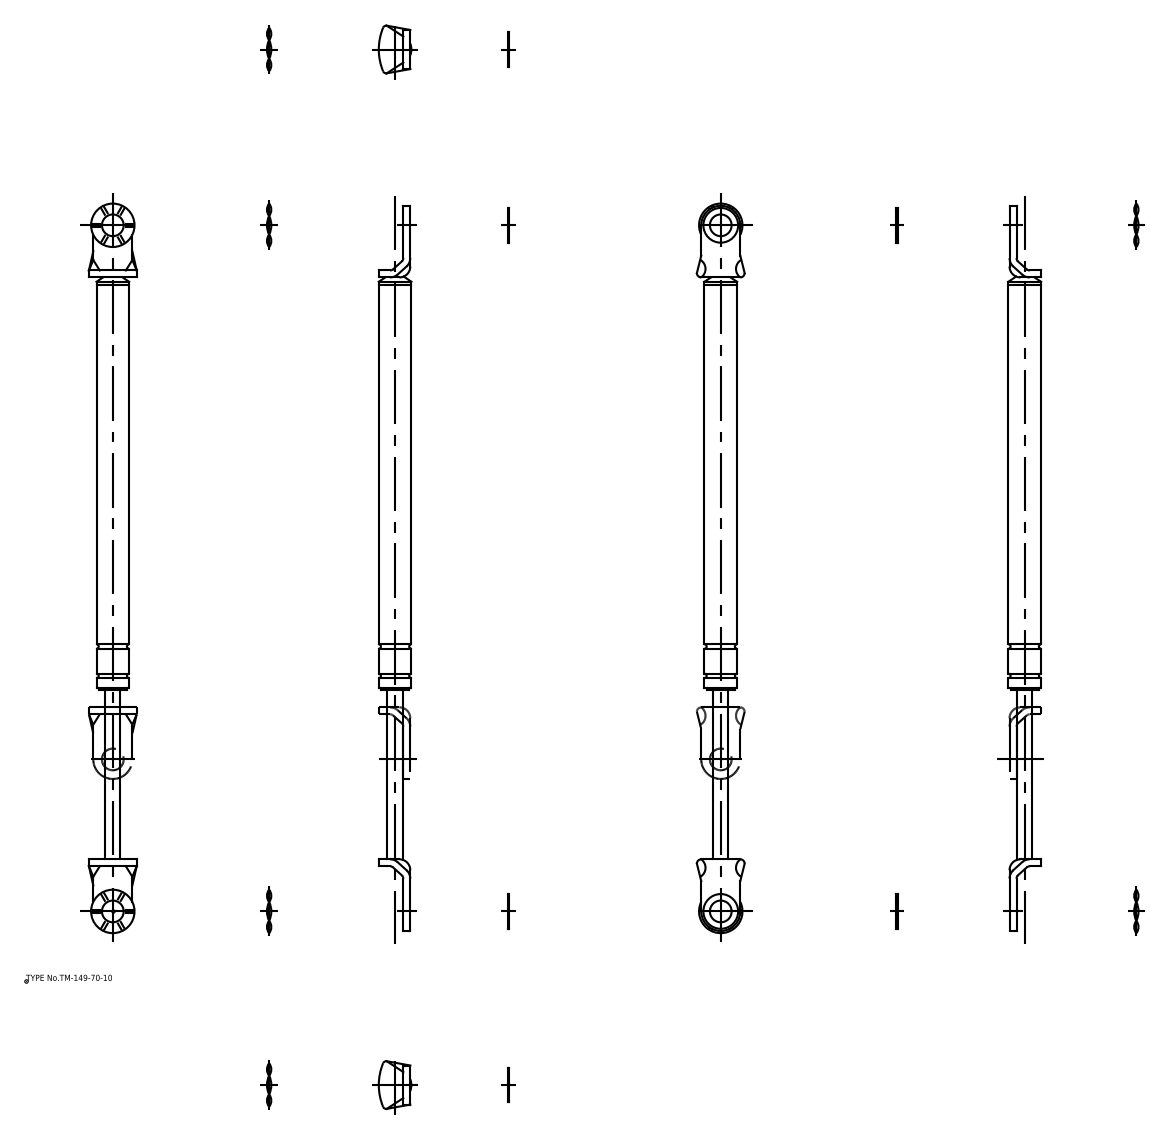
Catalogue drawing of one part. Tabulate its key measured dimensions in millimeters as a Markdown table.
| quantity | value |
| --- | --- |
| part name | washer_2; washer_1; body_div |
| STEP written by | spGate 16.7.1 (AUTOMOTIVE_DESIGN) |
| units | millimeters |
| bodies | 6 solids, 92 faces (44 planar, 42 cylindrical, 6 other) |
| overall size | 336 × 22 × 15.4 |
| volume | 41 872 mm³ |
| surface area | 16 547 mm² |
| round holes (diameter × count) | 10 × 2 |
| round bosses / shafts (diameter × count) | 20 × 2, 16 × 2, 15.4 × 1, 15 × 1, 13 × 1, 7 × 1 |
| partial cylindrical surfaces (radius × count) | 2 × 2, 5 × 2, 9 × 2, 17.12 × 1 |
| main face-to-face distances | 3.2, 2, 5.2, 271.2, 0.5, 3.7, 5.7, 274.4, 81.2, 193.2 |
| hole center spacings | 316 |
